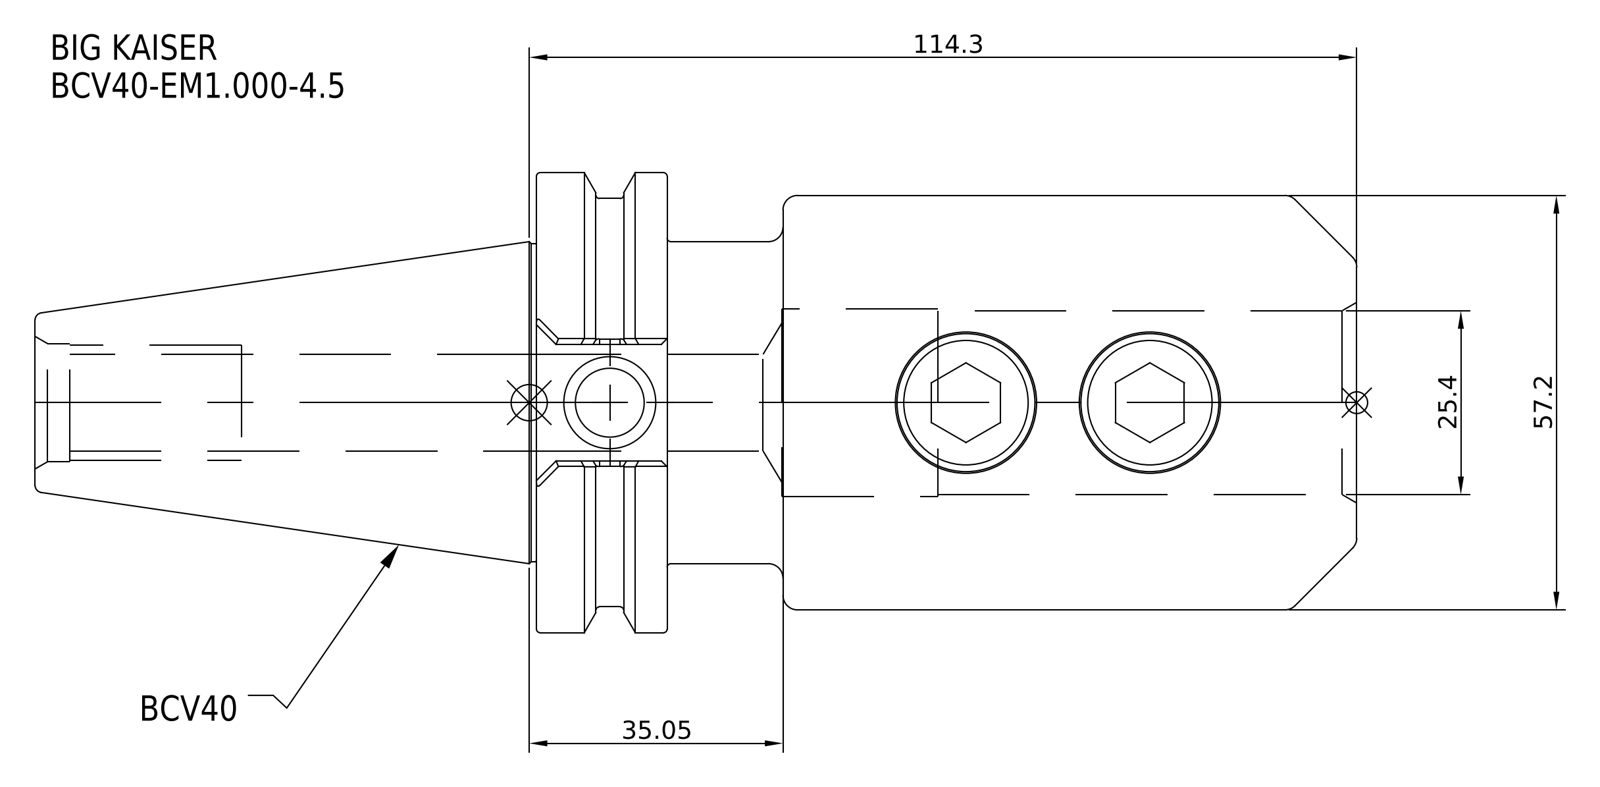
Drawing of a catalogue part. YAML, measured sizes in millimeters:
part_name: "BCV40-EM1_000-4_5"
step_written_by: "SolidWorks 2021 (CONFIG_CONTROL_DESIGN)"
units: millimeters
bodies: {solids: 1, faces: 30, planar: 8, cylindrical: 14, other: 8}
overall_size: [182.55, 63.5, 63.5]
volume: 302497
surface_area: 41023
round_holes:
  - {diameter: 25.4, count: 1}
round_bosses_or_shafts:
  - {diameter: 63.5, count: 1}
  - {diameter: 57.2, count: 1}
  - {diameter: 56.36, count: 1}
  - {diameter: 44.45, count: 1}
face_to_face_distances: [18.05, 16, 34.05, 79.25, 95.25, 113.3, 182.55, 103.3, 87.3, 69.25]
